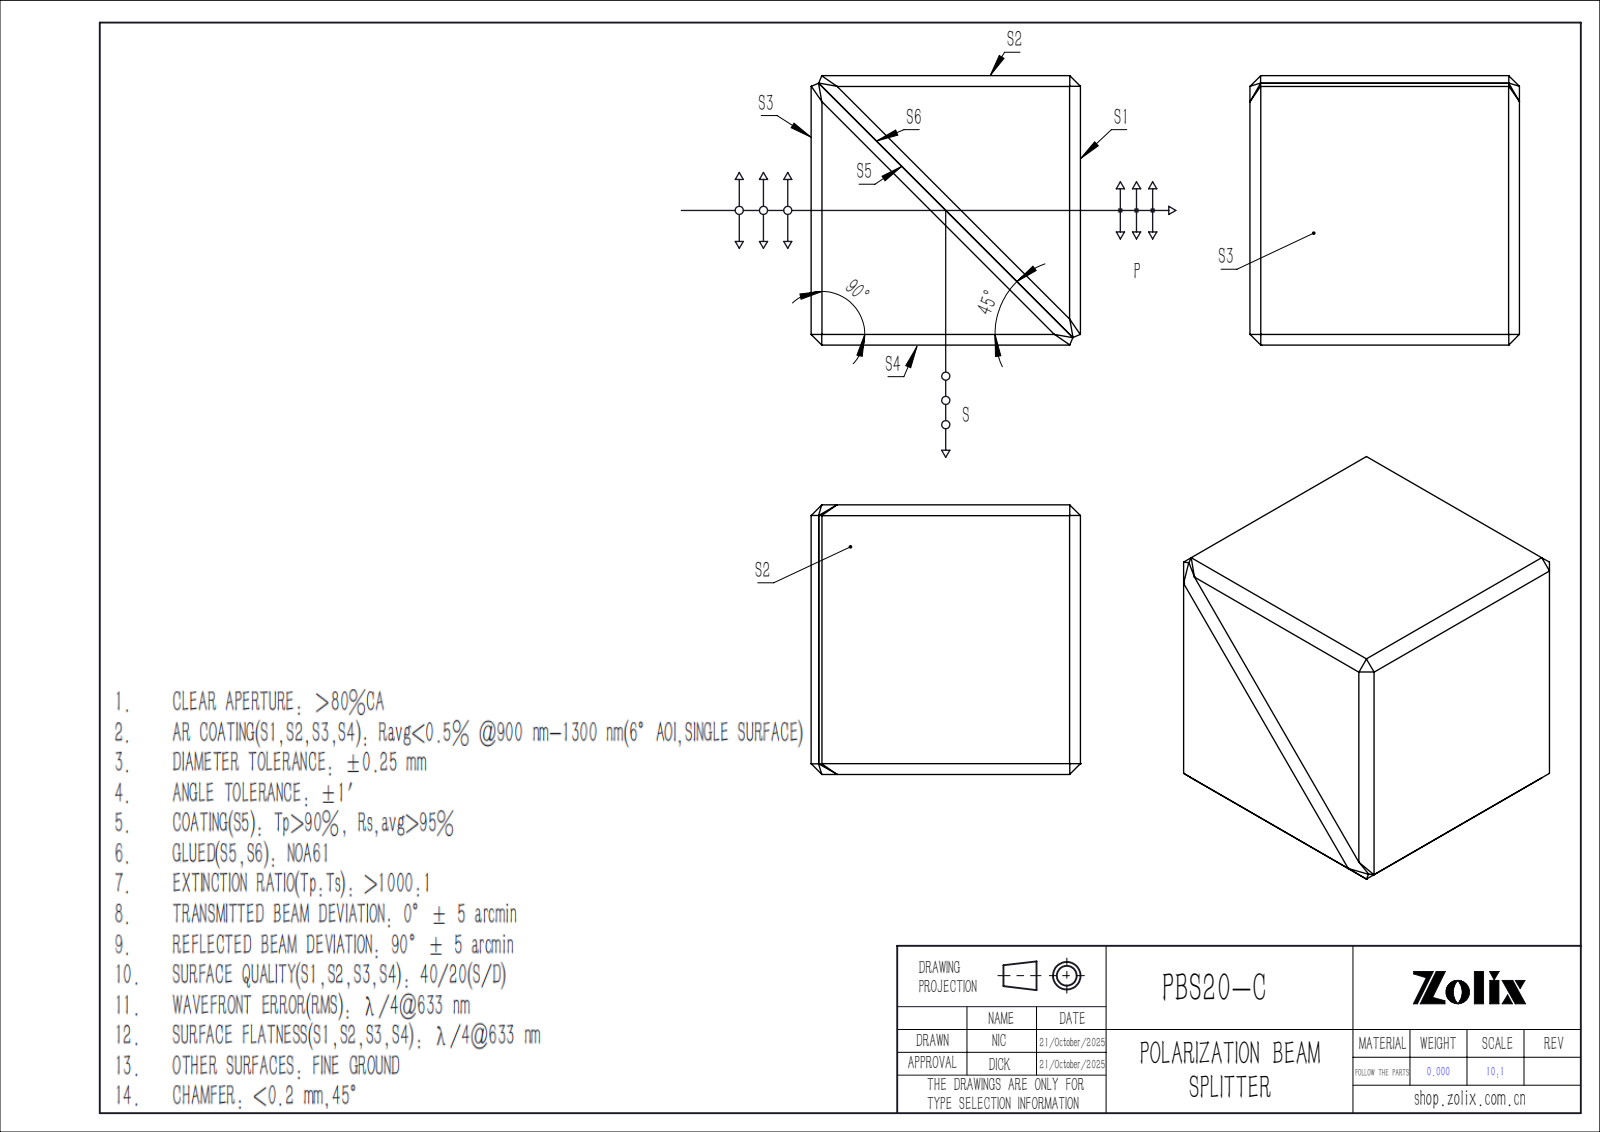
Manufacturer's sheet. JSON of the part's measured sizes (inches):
{"part_name": "PBS633-1-2; PBS633-1-1; PBS633", "step_written_by": "SolidWorks 2022 (CONFIG_CONTROL_DESIGN)", "units": "inches", "bodies": {"solids": 2, "faces": 43, "planar": 41, "cylindrical": 2, "other": 0}, "overall_size": [0.787, 0.787, 0.787], "volume_in3": 0.488, "surface_area_in2": 5.388, "round_holes": [[0.016, 1]], "face_to_face_distances": [0.787, 1.102, 0.546, 1.015, 0.551, 1.102, 0.551, 0.031, 0.756, 1.178]}
